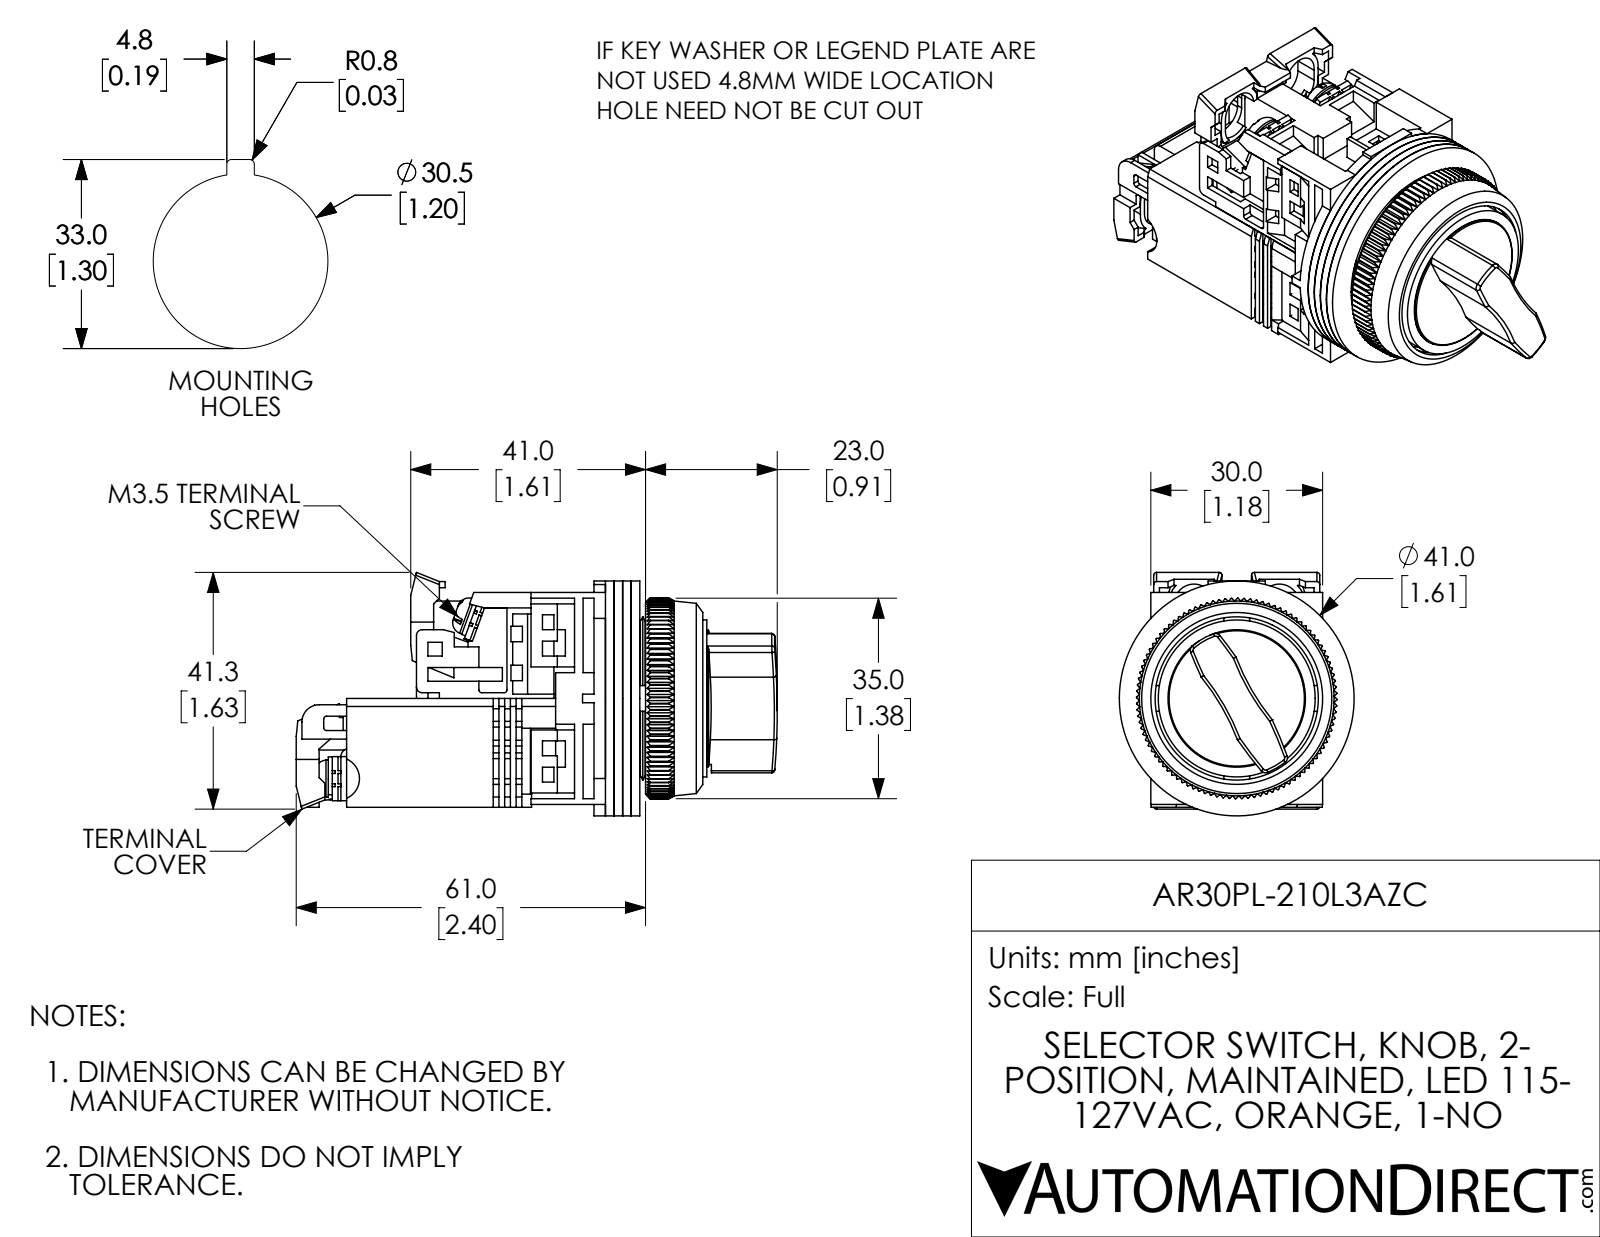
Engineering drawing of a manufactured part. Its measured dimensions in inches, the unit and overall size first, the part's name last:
Units: inches
Overall size (bounding box): 3.307 × 1.673 × 1.614
Round holes (diameter × count): ⌀0.138 ×6, ⌀0.142 ×4, ⌀0.118 ×3, ⌀0.472 ×1, ⌀0.709 ×1, ⌀0.768 ×1, ⌀0.827 ×1, ⌀1.122 ×1, ⌀1.181 ×1, ⌀1.252 ×1
Round bosses / shafts (diameter × count): ⌀0.26 ×4, ⌀0.138 ×2, ⌀0.063 ×2, ⌀1.614 ×1, ⌀1.15 ×1, ⌀1.079 ×1, ⌀0.945 ×1, ⌀0.886 ×1
Partial cylindrical surfaces — rounded edges, fillets, slot ends (radius × count): R0.059 ×17, R0.02 ×13, R0.039 ×6, R0.138 ×4, R0.177 ×4, R0.118 ×2, R1.575 ×2, R2.953 ×2
Main face-to-face distances: 0.059, 0.118, 0.177, 0.079, 0.039, 0.748, 0.787, 0.197, 0.256, 1.417
Hole centre spacings: 0.579, 0.297, 0.624, 0.02, 0.302, 0.583, 0.583, 0.606
Volume: 3.001 in³ · Surface area: 63.38 in²
Bodies: 27 solids, 2357 faces (1706 planar, 321 cylindrical, 330 other)
Part name (STEP PRODUCT): AR30PL-210L3AZC
STEP written by: SolidWorks 2017 (AUTOMOTIVE_DESIGN)
